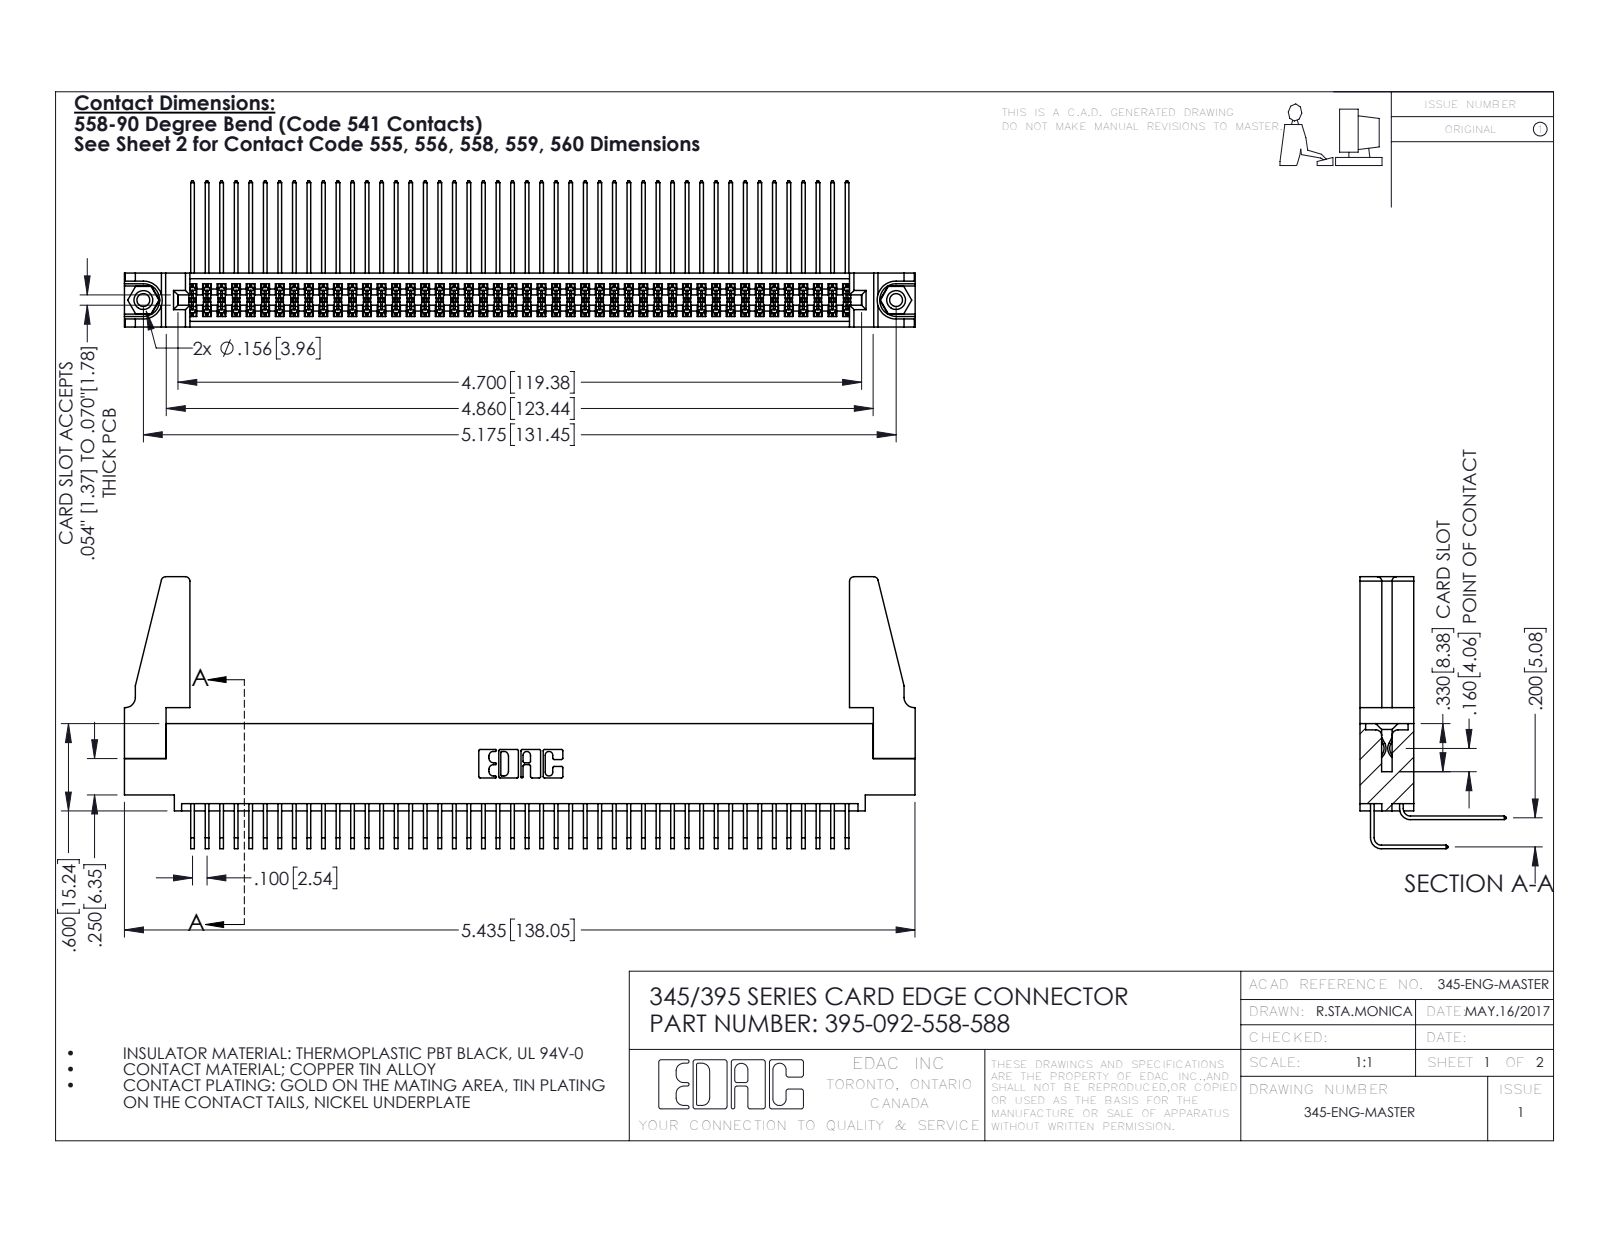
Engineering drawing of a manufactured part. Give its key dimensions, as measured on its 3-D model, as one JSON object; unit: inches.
{"part_name": "345 Part_0.110 Offset - 0.156 Dia-TH; 345-292-001_558 559 Tail - 1; 395-092-558-588; 345-250-001_345-250-001-102 (+2 more)", "step_written_by": "SolidWorks 2016 (CONFIG_CONTROL_DESIGN)", "units": "inches", "bodies": {"solids": 97, "faces": 5038, "planar": 3376, "cylindrical": 1646, "other": 16}, "overall_size": [5.436, 1.869, 1.005], "volume_in3": 1.047, "surface_area_in2": 40.84, "round_holes": [[0.089, 2], [0.125, 2], [0.156, 2], [0.064, 1]], "round_bosses_or_shafts": [[0.155, 2]], "partial_cylinders_radius": [[0.006, 139], [0.01, 22], [0.03, 8], [0.007, 6], [0.031, 6], [0.026, 3], [0.014, 2], [0.019, 2]], "face_to_face_distances": [0.072, 0.298, 0.2, 0.37, 0.098, 0.272, 0.025, 0.225, 0.025, 0.175], "hole_center_spacings": [0.27, 4.939, 5.175]}
